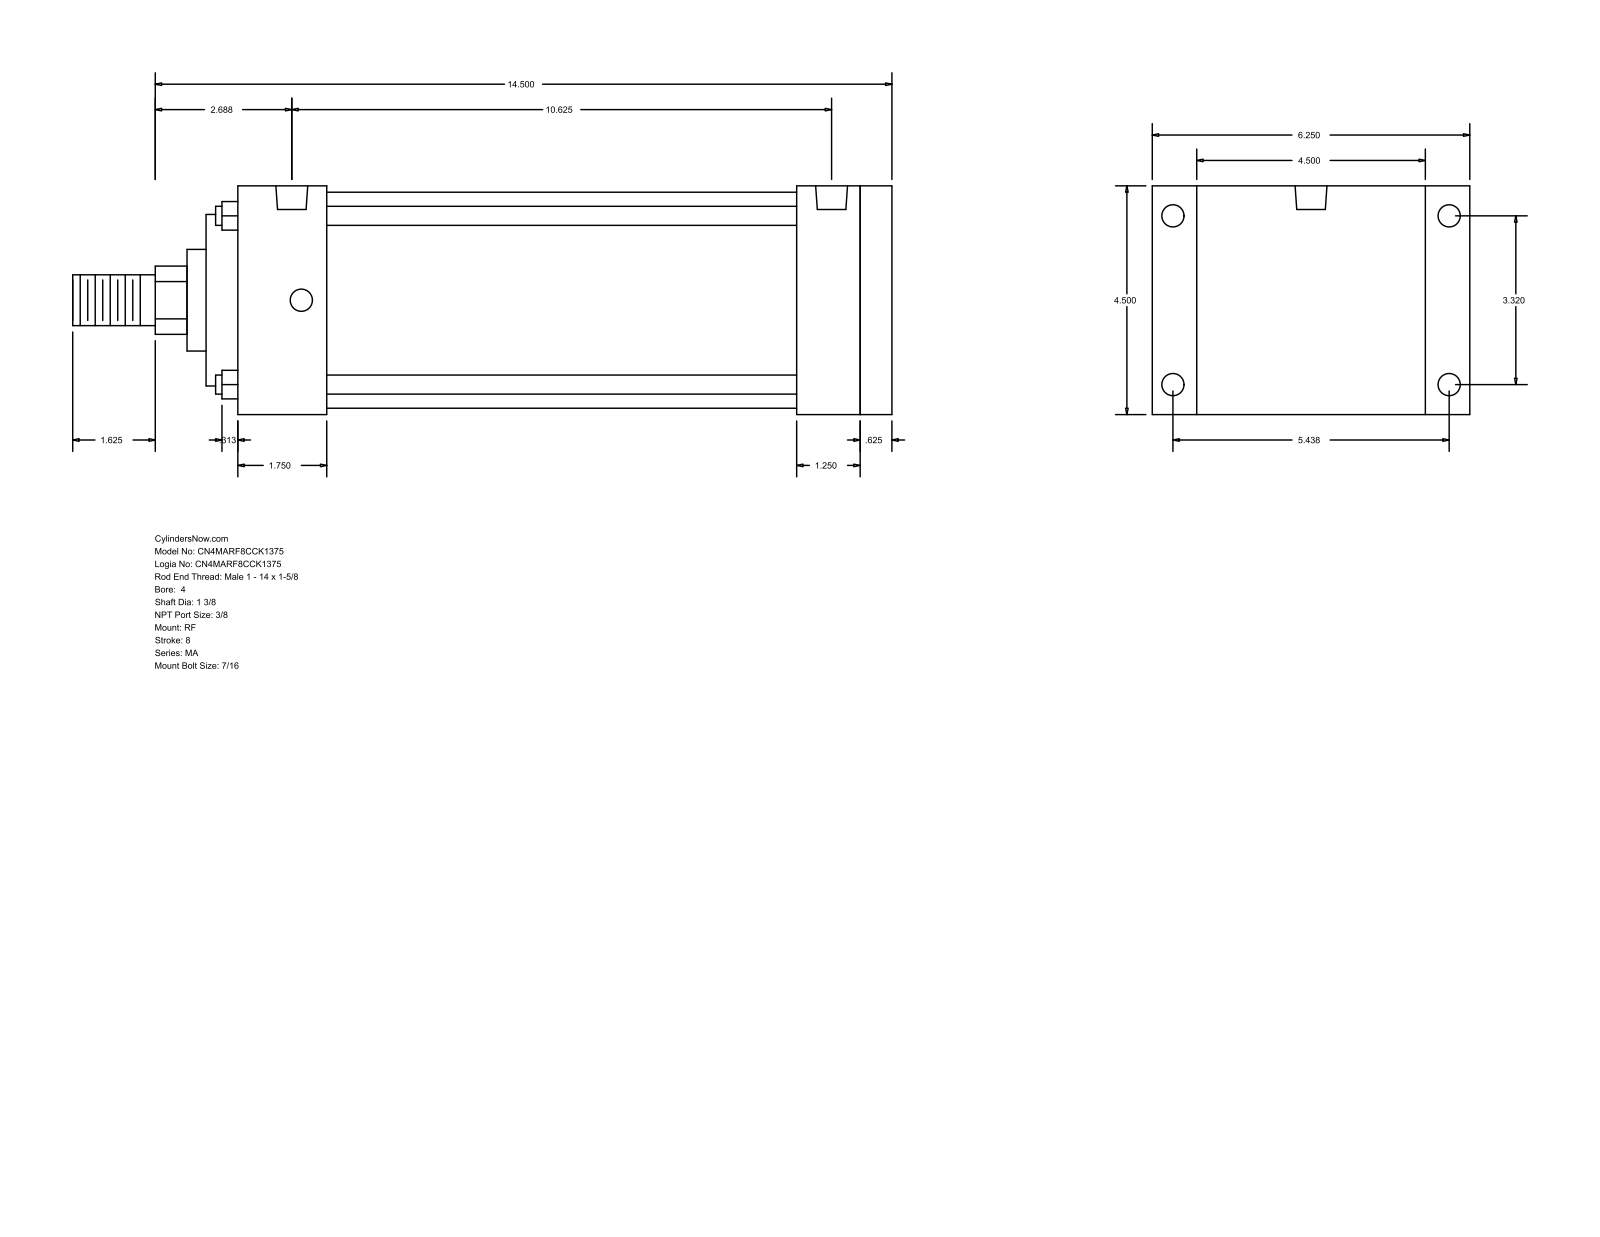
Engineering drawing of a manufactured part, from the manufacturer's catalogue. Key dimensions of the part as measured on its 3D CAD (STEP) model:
Part name (STEP PRODUCT): MA_RF__0400_1.375
STEP written by: GSSL Pune (CONFIG_CONTROL_DESIGN)
Units: millimetres
Bodies: 0 solids, 94 faces (65 planar, 29 cylindrical, 0 other)
Overall size (bounding box): 409.57 × 158.75 × 114.3
Round holes (diameter × count): ⌀11.11 ×8, ⌀15.93 ×2
Round bosses / shafts (diameter × count): ⌀9.53 ×4, ⌀107.95 ×1, ⌀85.72 ×1, ⌀50.8 ×1, ⌀34.92 ×1, ⌀25.4 ×1
Partial cylindrical surfaces — rounded edges, fillets, slot ends (radius × count): R17.06 ×1
Main face-to-face distances: 114.3, 327.03, 15.87, 311.16, 342.9, 22.23, 136.53, 295.28, 279.41, 31.75
Hole centre spacings: 84.32, 138.12, 161.82, 260.35, 4.76, 4.77, 265.11, 265.12
